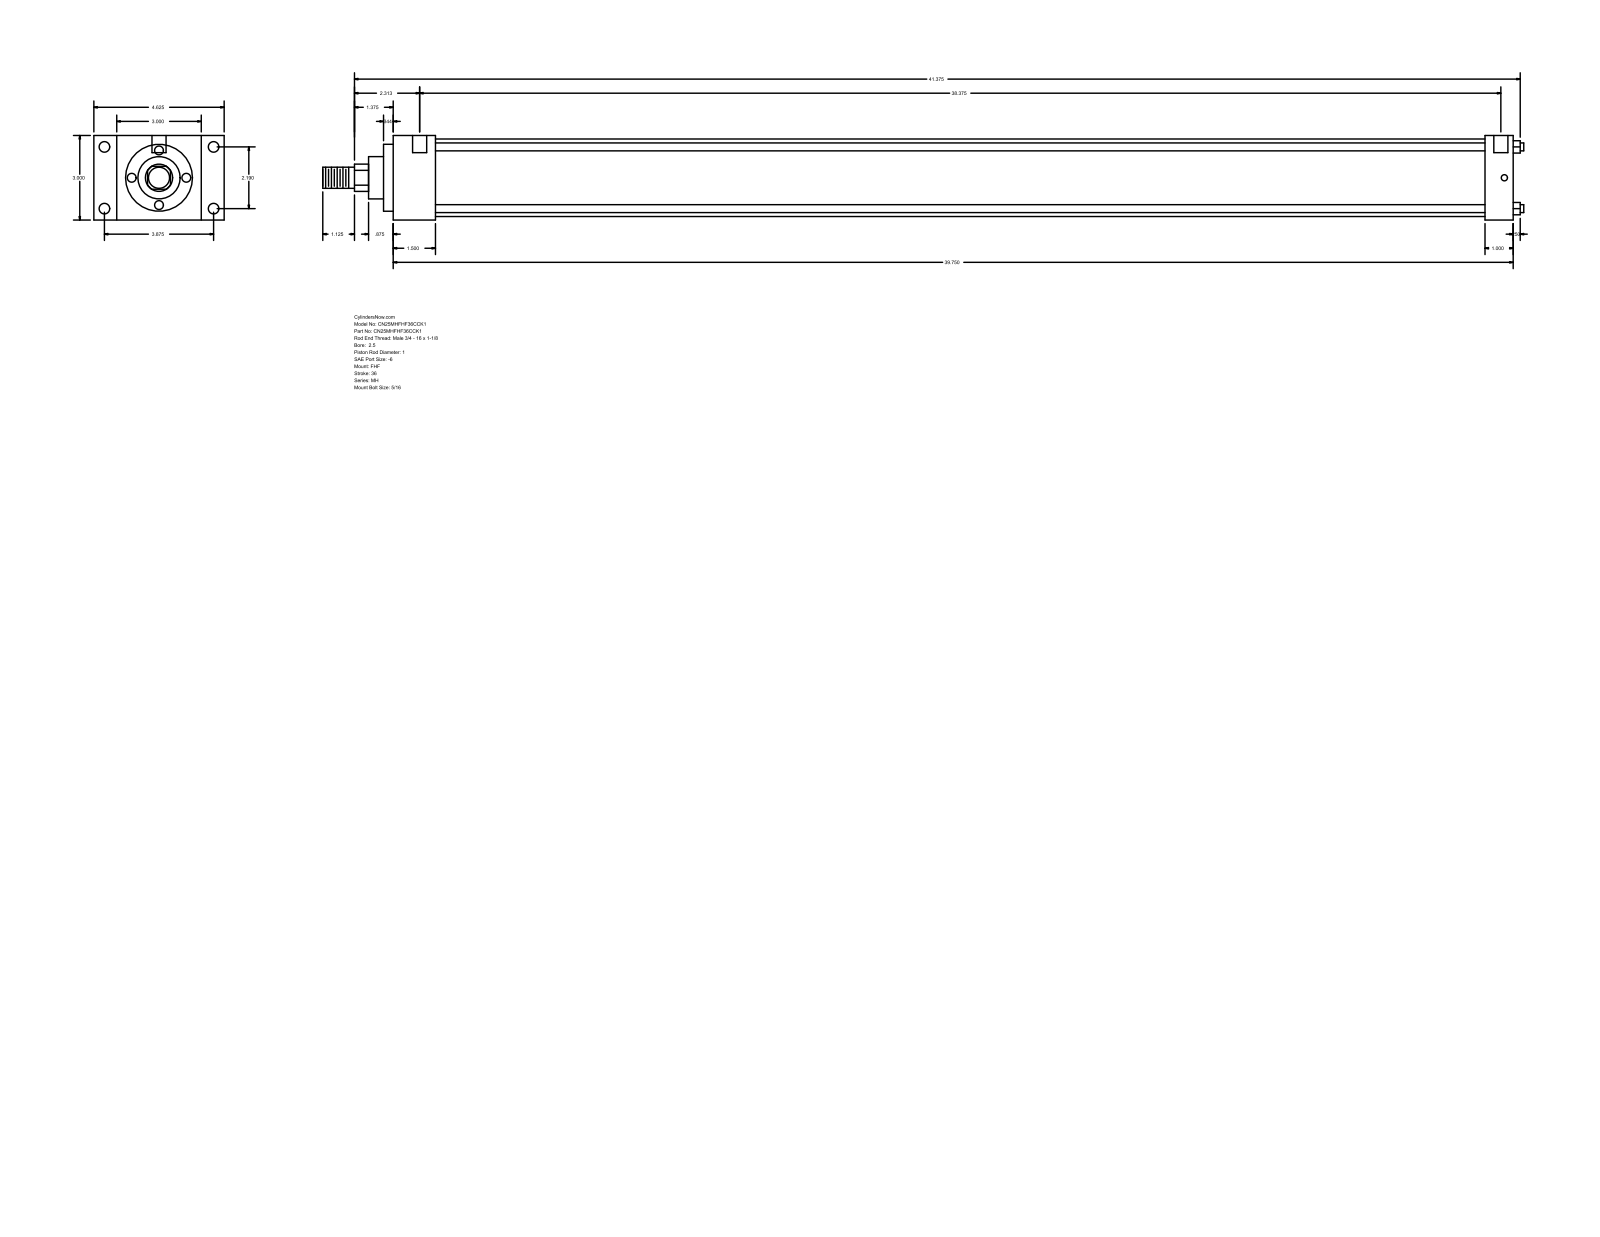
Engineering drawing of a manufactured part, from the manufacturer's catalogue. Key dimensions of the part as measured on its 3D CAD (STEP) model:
Part name (STEP PRODUCT): MH_FHF__0250_1
STEP written by: GSSL Pune (CONFIG_CONTROL_DESIGN)
Units: millimetres
Bodies: 0 solids, 90 faces (61 planar, 29 cylindrical, 0 other)
Overall size (bounding box): 1082.67 × 117.47 × 76.2
Round holes (diameter × count): ⌀5.56 ×4, ⌀9.53 ×4, ⌀12.7 ×2
Round bosses / shafts (diameter × count): ⌀7.14 ×4, ⌀69.85 ×1, ⌀60.33 ×1, ⌀38.1 ×1, ⌀25.4 ×1, ⌀19.05 ×1
Partial cylindrical surfaces — rounded edges, fillets, slot ends (radius × count): R12.29 ×1
Main face-to-face distances: 76.2, 1009.66, 38.11, 971.55, 20.64, 96.84, 117.48, 984.25, 946.14, 25.41
Hole centre spacings: 55.62, 98.42, 113.05, 982.66, 3.18, 4.76, 974.72, 977.9
